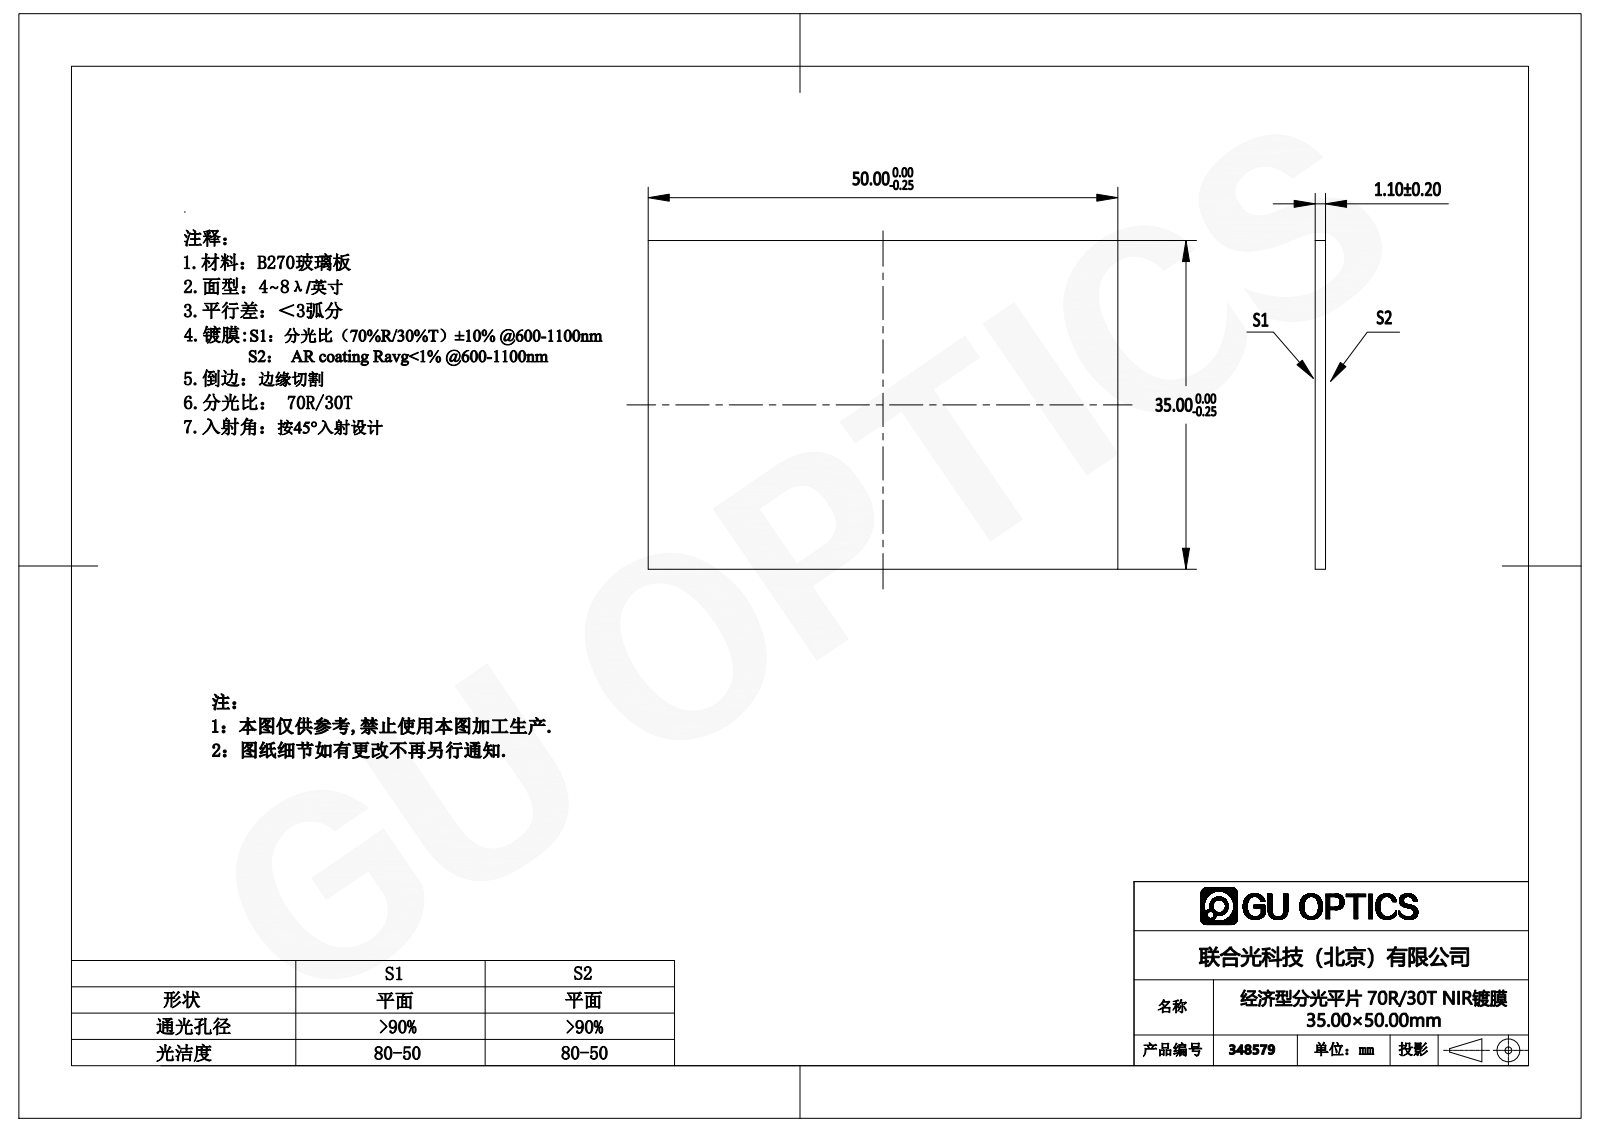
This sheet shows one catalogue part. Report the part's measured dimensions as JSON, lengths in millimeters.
{"part_name": "348509", "step_written_by": "SolidWorks 2016 (CONFIG_CONTROL_DESIGN)", "units": "millimeters", "bodies": {"solids": 1, "faces": 6, "planar": 6, "cylindrical": 0, "other": 0}, "overall_size": [50, 35, 1.1], "volume_mm3": 1925, "surface_area_mm2": 3687, "face_to_face_distances": [1.1, 35, 50]}
